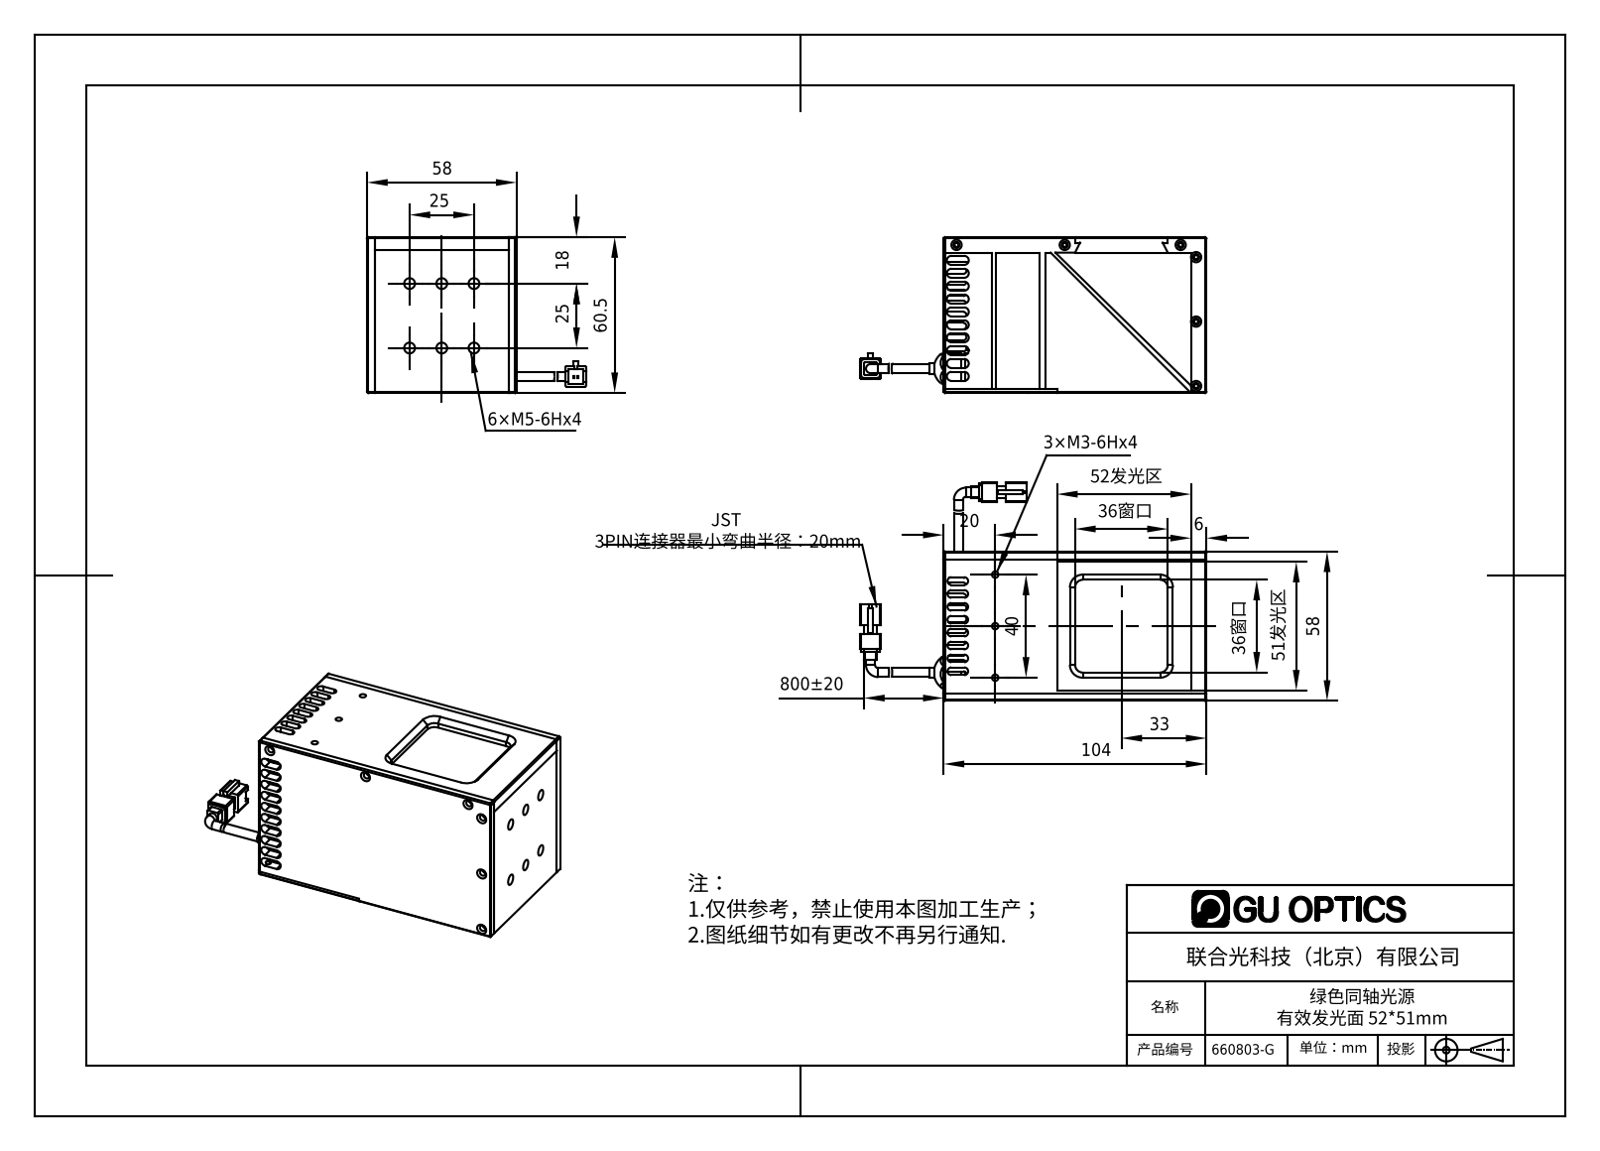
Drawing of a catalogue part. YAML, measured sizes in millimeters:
part_name: "绿色同轴光源 有效发光面 5251mm"
step_written_by: "SolidWorks 2016 (AUTOMOTIVE_DESIGN)"
units: millimeters
bodies: {solids: 22, faces: 1568, planar: 921, cylindrical: 491, other: 156}
overall_size: [134.4, 60.7, 58]
volume: 118035
surface_area: 91224
round_holes:
  - {diameter: 1.6, count: 13}
  - {diameter: 2, count: 10}
  - {diameter: 2.4, count: 10}
  - {diameter: 4, count: 6}
  - {diameter: 4.2, count: 6}
  - {diameter: 2.2, count: 5}
  - {diameter: 2.5, count: 3}
  - {diameter: 6.8, count: 1}
round_bosses_or_shafts:
  - {diameter: 3.5, count: 2}
  - {diameter: 9.76, count: 1}
  - {diameter: 8, count: 1}
  - {diameter: 4, count: 1}
partial_cylinders:
  - {radius: 1.25, count: 20}
  - {radius: 1.75, count: 20}
  - {radius: 1.5, count: 16}
  - {radius: 0.5, count: 8}
  - {radius: 1, count: 4}
  - {radius: 3, count: 4}
  - {radius: 4, count: 1}
  - {radius: 6.25, count: 1}
face_to_face_distances: [4, 54, 2, 55, 1, 58, 3, 51, 58.5, 6]
hole_center_spacings: [25, 12.5, 20, 27.95, 30, 3.58, 5.51, 9.03]
